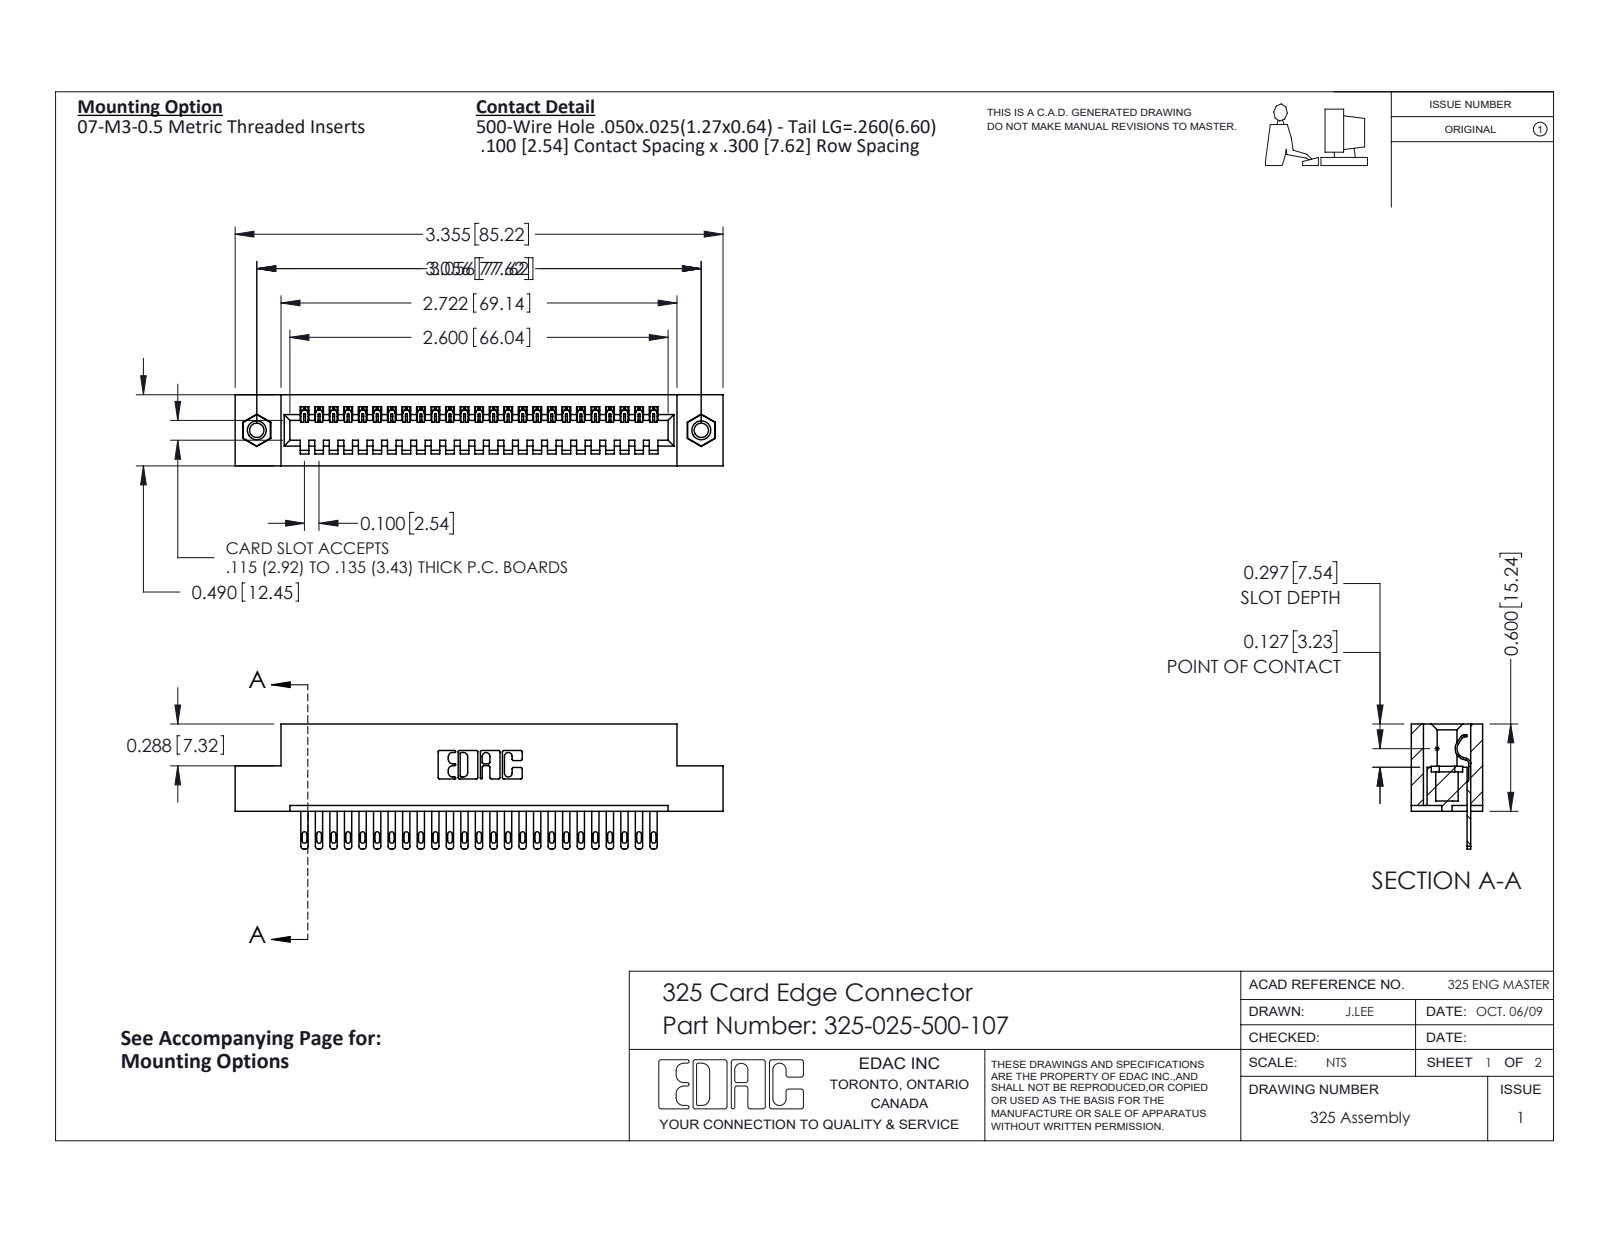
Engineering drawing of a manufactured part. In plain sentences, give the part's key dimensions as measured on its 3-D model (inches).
The part is named "325-292-001_325-293-100; 325 Part_TI; 325-025-500-107; 345-250-001_345-250-005-103". Its 3-D file was written by "SolidWorks 2016 (CONFIG_CONTROL_DESIGN)". It is 28 solids with 1524 faces: 1002 planar, 506 cylindrical and 16 other. Overall it measures 3.355 by 0.86 by 0.49 inches. Its volume is 0.652 cubic inches and its surface area 17.78 square inches. Round holes: 2 of diameter 0.098, 2 of diameter 0.125, 2 of diameter 0.16. Round bosses or shafts: 2 of diameter 0.155. Partial cylindrical surfaces (rounded edges, fillets, slot ends): 50 of radius 0.006, 50 of radius 0.016, 50 of radius 0.02, 22 of radius 0.01, 6 of radius 0.007, 6 of radius 0.031, 3 of radius 0.026, 1 of radius 0.014. The main face-to-face distances are 0.083, 0.407, 0.49, 0.3, 0.107, 0.383, 0.025, 0.04, 0.325, 0.1. The hole center spacings are 3.056.
